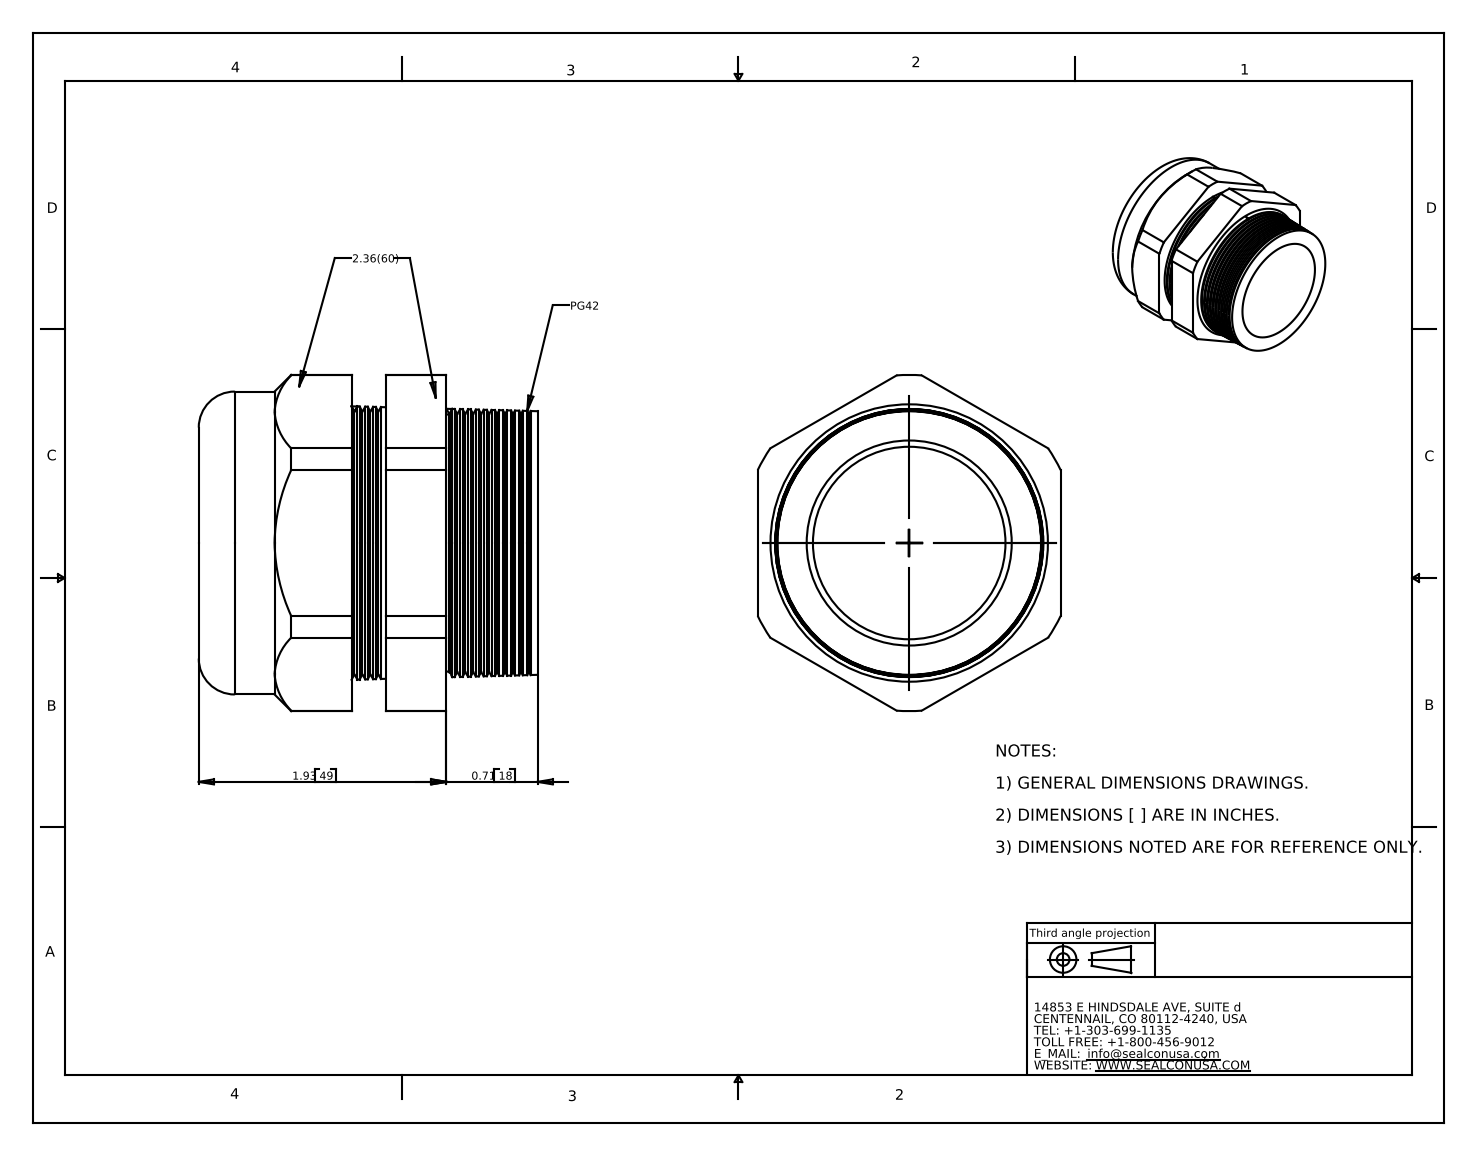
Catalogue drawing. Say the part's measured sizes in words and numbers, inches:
The part is named "CD42CA-GY". Its 3-D file was written by "SolidWorks 2007 (CONFIG_CONTROL_DESIGN)". It is 2 solids with 152 faces: 20 planar, 22 cylindrical and 110 other. Overall it measures 2.64 by 2.62 by 2.36 inches. Its volume is 6 cubic inches and its surface area 49.22 square inches. Round holes: 1 of diameter 1.5, 1 of diameter 1.597. Round bosses or shafts: 1 of diameter 2.36. Partial cylindrical surfaces (rounded edges, fillets, slot ends): 1 of radius 1.31. The main face-to-face distances are 2.36, 1.182, 0.267, 1.45, 0.74, 0.472, 0.71, 1.191, 1.458, 1.93.
